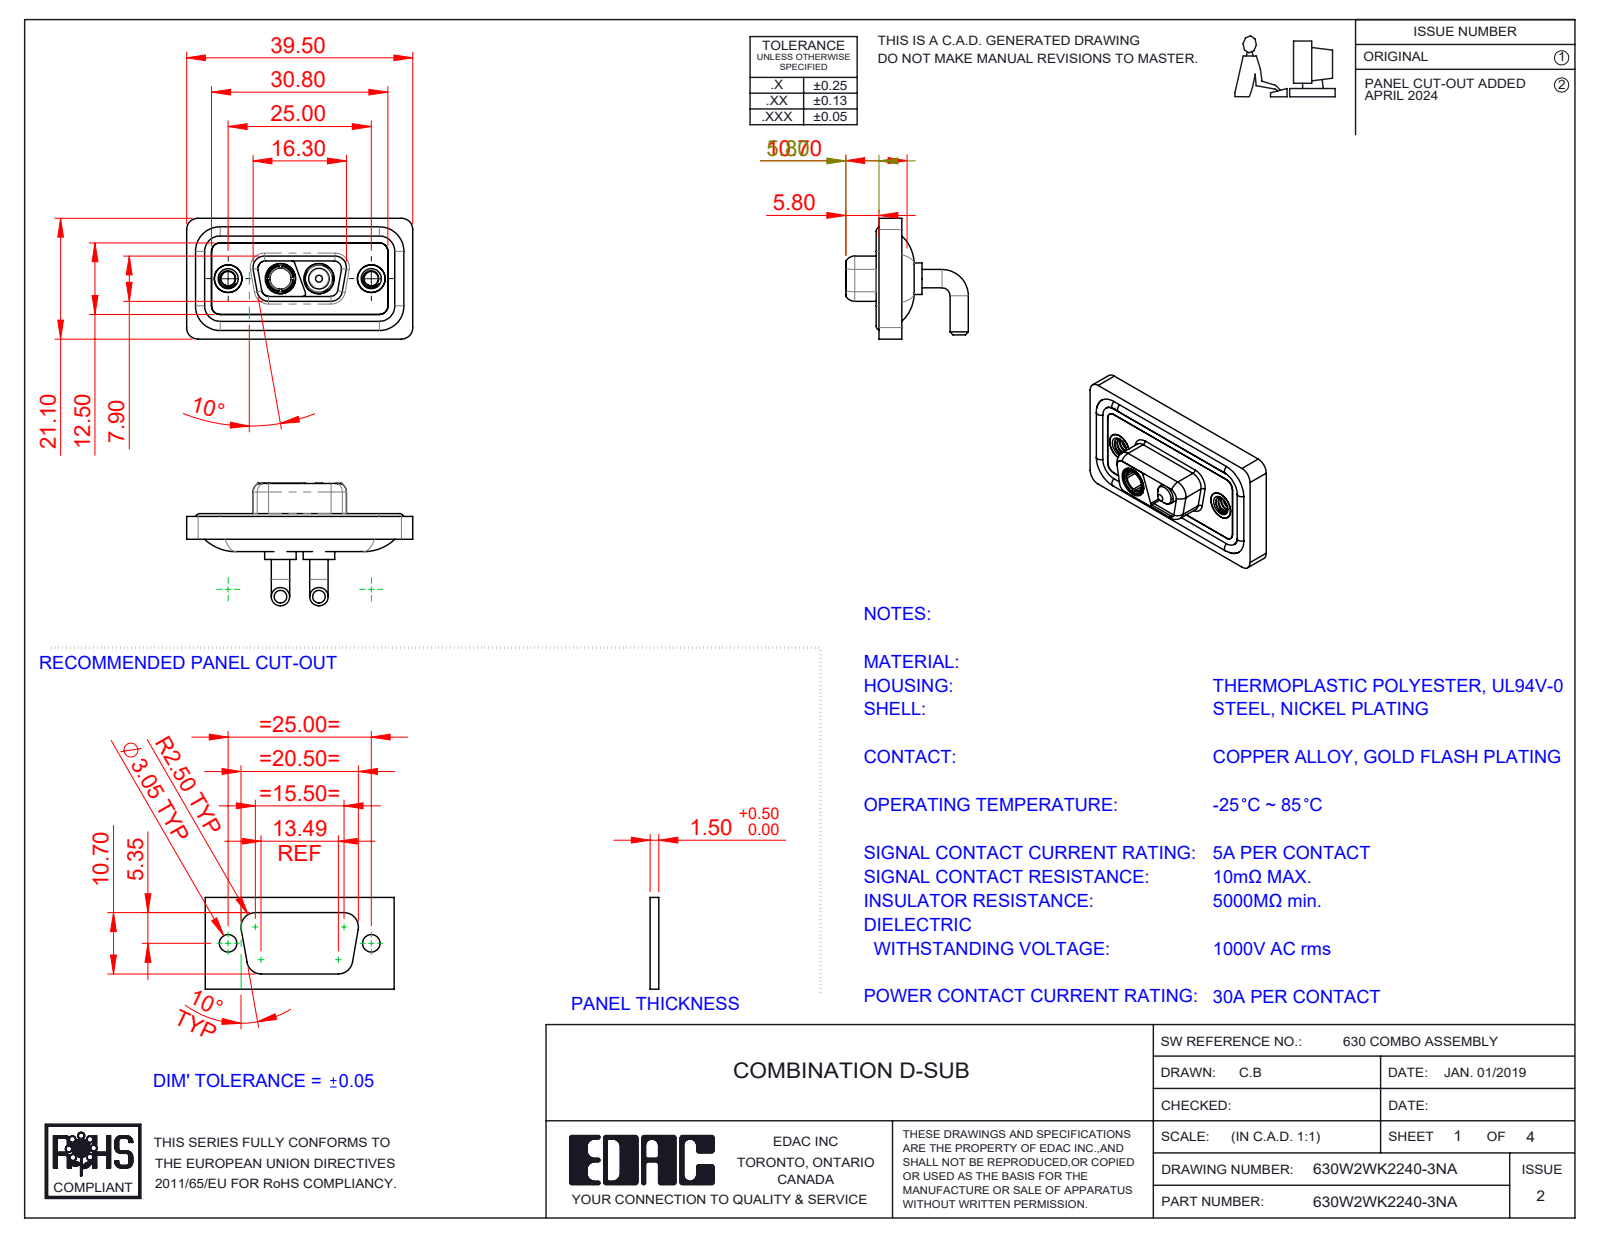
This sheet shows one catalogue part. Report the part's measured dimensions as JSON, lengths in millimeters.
{"part_name": "630Combo Threaded Rivet_A; 630W2WK2240-3NA; 630Combo Housing_2WK2; 630Combo Waterproof Housing_09 Contacts (+4 more)", "step_written_by": "SolidWorks 2023 (CONFIG_CONTROL_DESIGN)", "units": "millimeters", "bodies": {"solids": 11, "faces": 502, "planar": 144, "cylindrical": 233, "other": 125}, "overall_size": [39.5, 21.4, 21.1], "volume_mm3": 4755, "surface_area_mm2": 7534, "round_holes": [[4.85, 4], [2.5, 2], [4, 2], [4.05, 2], [5, 2], [5.3, 2], [3.7, 1]], "round_bosses_or_shafts": [[3.2, 4], [1.6, 4], [5.5, 2], [5.2, 2], [4.95, 2], [4.8, 2], [4.75, 2], [3.75, 2]], "partial_cylinders_radius": [[1.5, 18], [2, 18], [1.35, 8], [1.6, 8], [0.5, 6], [0.25, 4], [0.6, 4], [0.65, 4]], "face_to_face_distances": [0.4, 1.1, 2.9, 1.8, 2.5, 1.6, 3.1, 1.5, 2.1, 3.7], "hole_center_spacings": [9.14, 15.86, 6.72, 25]}
